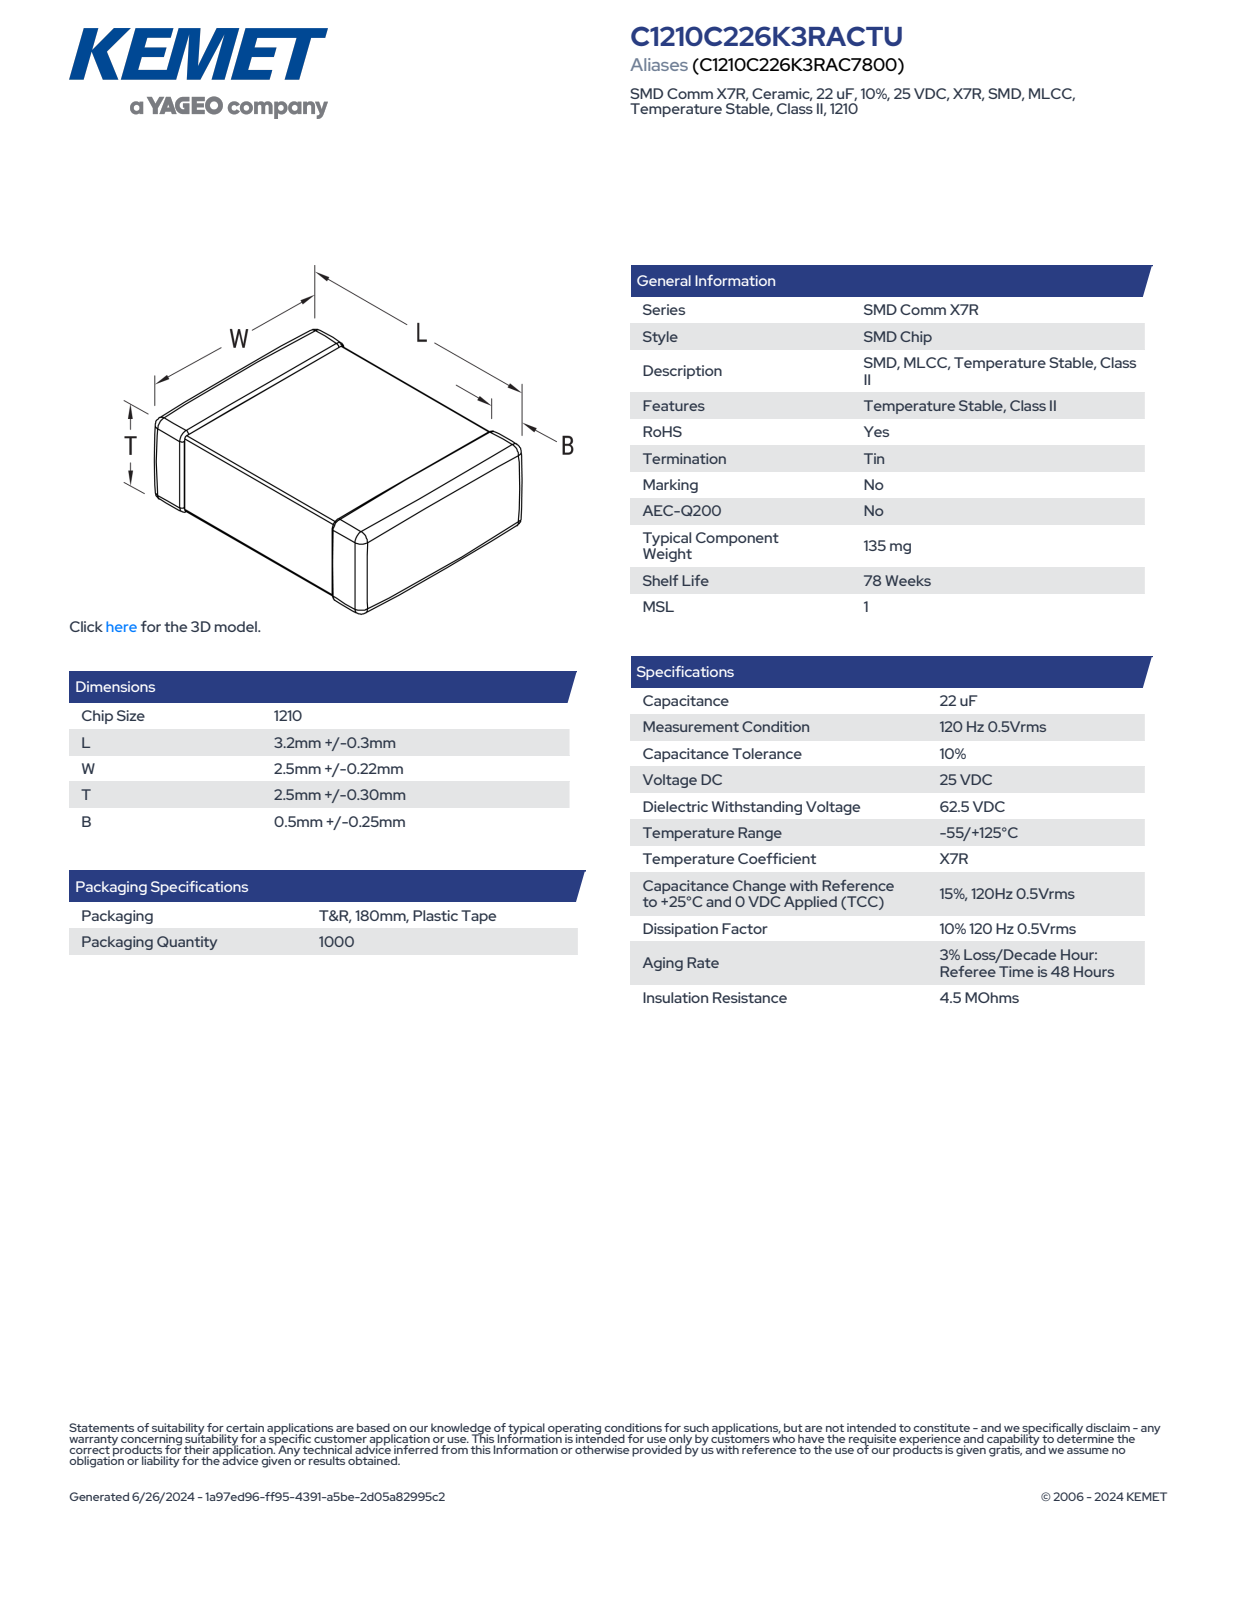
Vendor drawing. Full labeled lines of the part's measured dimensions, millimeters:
Part name (STEP PRODUCT): CCS_CCSTD_1210_L3.5W2.72T2.8B0.5
STEP written by: SolidWorks 2021 (AUTOMOTIVE_DESIGN)
Units: millimetres
Bodies: 4 solids, 125 faces (71 planar, 38 cylindrical, 16 other)
Overall size (bounding box): 3.5 × 2.8 × 2.72
Volume: 25 mm³ · Surface area: 54 mm²
Main face-to-face distances: 3.5, 2.66, 2.74, 2.6, 2.68, 2.72, 2.8, 2.75, 2.69, 1.49
